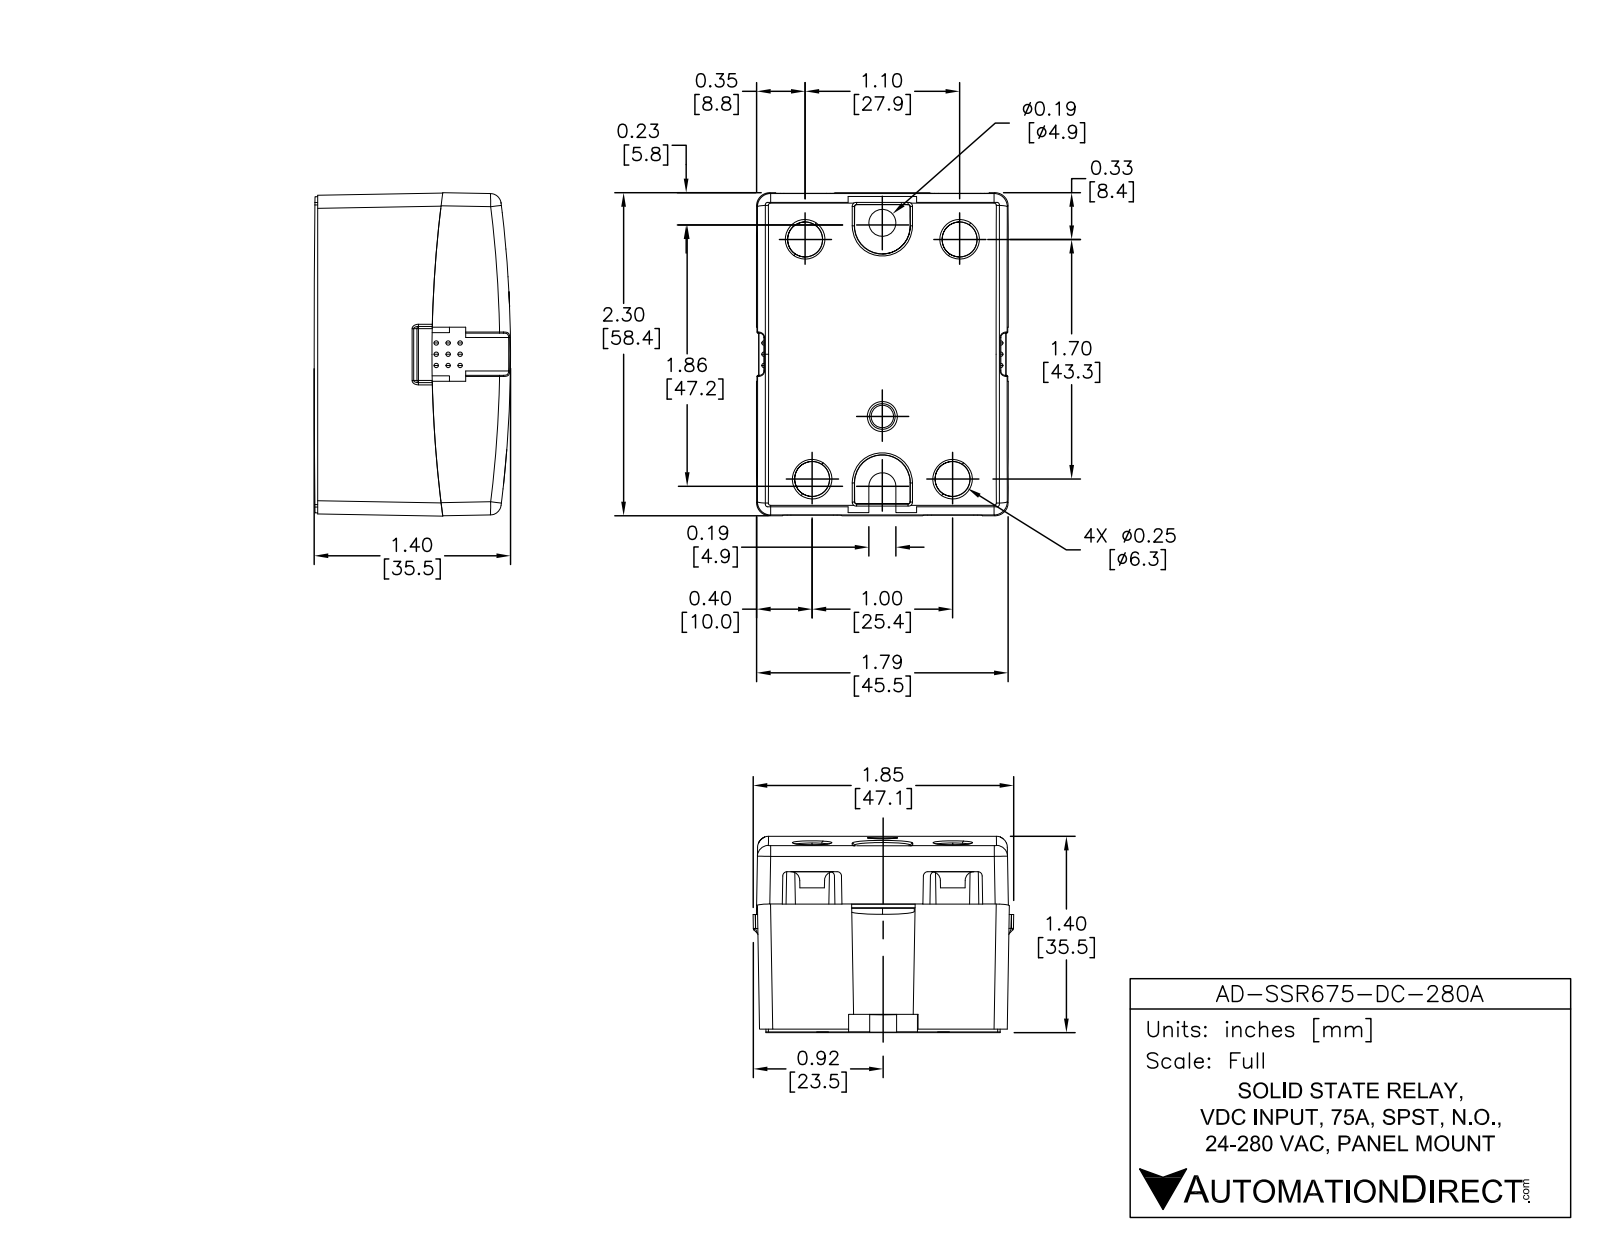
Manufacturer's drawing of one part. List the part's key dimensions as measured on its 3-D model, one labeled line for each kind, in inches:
Part name (STEP PRODUCT): AD-SSR675-DC-280A
STEP written by: SolidWorks 2013 (AUTOMOTIVE_DESIGN)
Units: inches
Bodies: 3 solids, 251 faces (145 planar, 95 cylindrical, 11 other)
Overall size (bounding box): 2.3 × 1.79 × 1.4
Volume: 5.14 in³ · Surface area: 26.41 in²
Round holes (diameter × count): ⌀0.25 ×4, ⌀0.19 ×1
Round bosses / shafts (diameter × count): ⌀0.4 ×2, ⌀0.35 ×2, ⌀0.3 ×2, ⌀0.25 ×2, ⌀0.2 ×2, ⌀0.2 ×2
Partial cylindrical surfaces — rounded edges, fillets, slot ends (radius × count): R0.03 ×6, R0.01 ×4, R0.04 ×4, R0.5 ×4, R0.194 ×2, R0.095 ×1, R0.5 ×1, R0.5 ×1
Main face-to-face distances: 1.79, 2.3, 1.166, 0.25, 0.916, 0.671, 1.059, 0.5, 1.8, 0.08
Hole centre spacings: 0.556, 0.565, 1, 1.1, 1.7, 1.701, 1.876, 1.879
